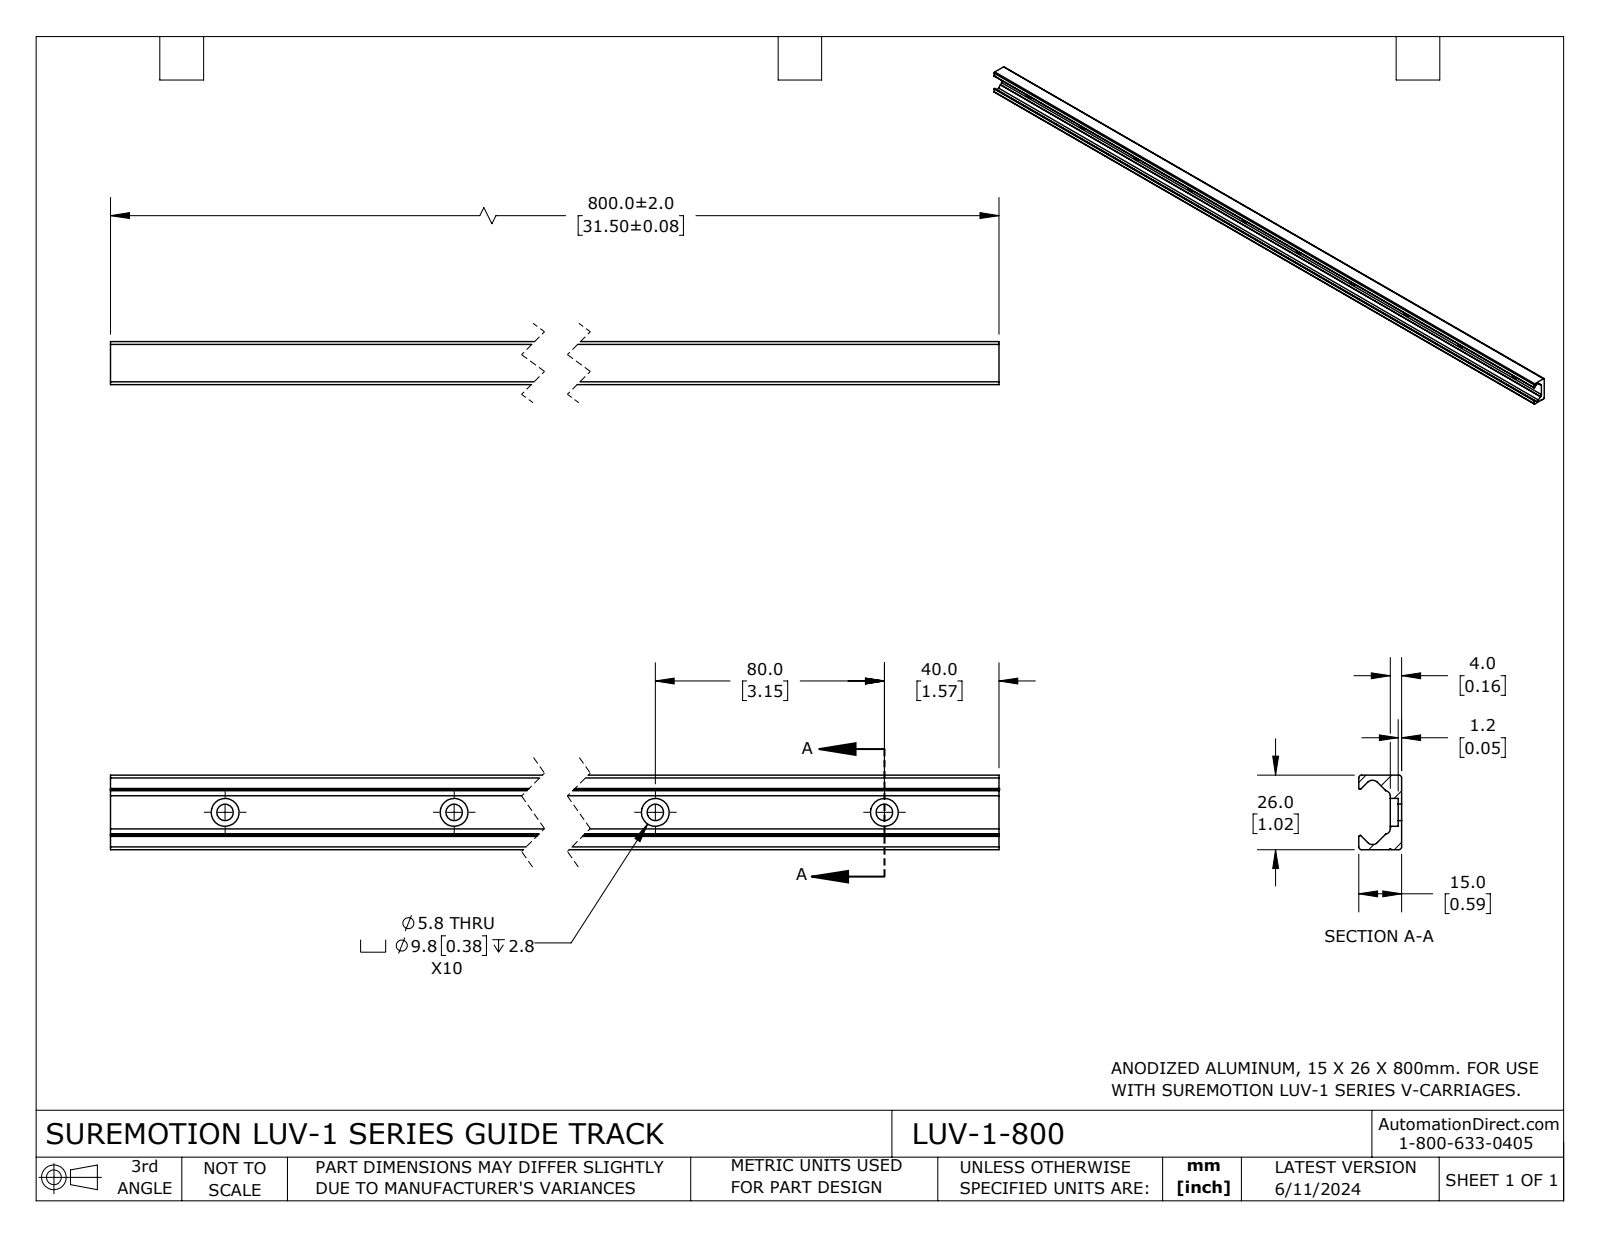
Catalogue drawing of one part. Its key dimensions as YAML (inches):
part_name: "LUV-1-800"
step_written_by: "SolidWorks 2023 (CONFIG_CONTROL_DESIGN)"
units: inches
bodies: {solids: 1, faces: 78, planar: 23, cylindrical: 55, other: 0}
overall_size: [31.496, 1.024, 0.591]
volume: 8.79
surface_area: 131.7
round_holes:
  - {diameter: 0.228, count: 10}
  - {diameter: 0.384, count: 10}
partial_cylinders:
  - {radius: 0.039, count: 4}
  - {radius: 0.02, count: 2}
  - {radius: 0.025, count: 2}
  - {radius: 0.03, count: 2}
  - {radius: 0.07, count: 2}
  - {radius: 0.094, count: 2}
  - {radius: 0.013, count: 1}
face_to_face_distances: [1.024, 0.158, 0.591, 0.433, 0.68, 0.048, 0.11, 0.544, 31.496]
hole_center_spacings: [3.15, 6.299, 9.449, 12.598, 15.748, 18.898, 22.047, 25.197]
